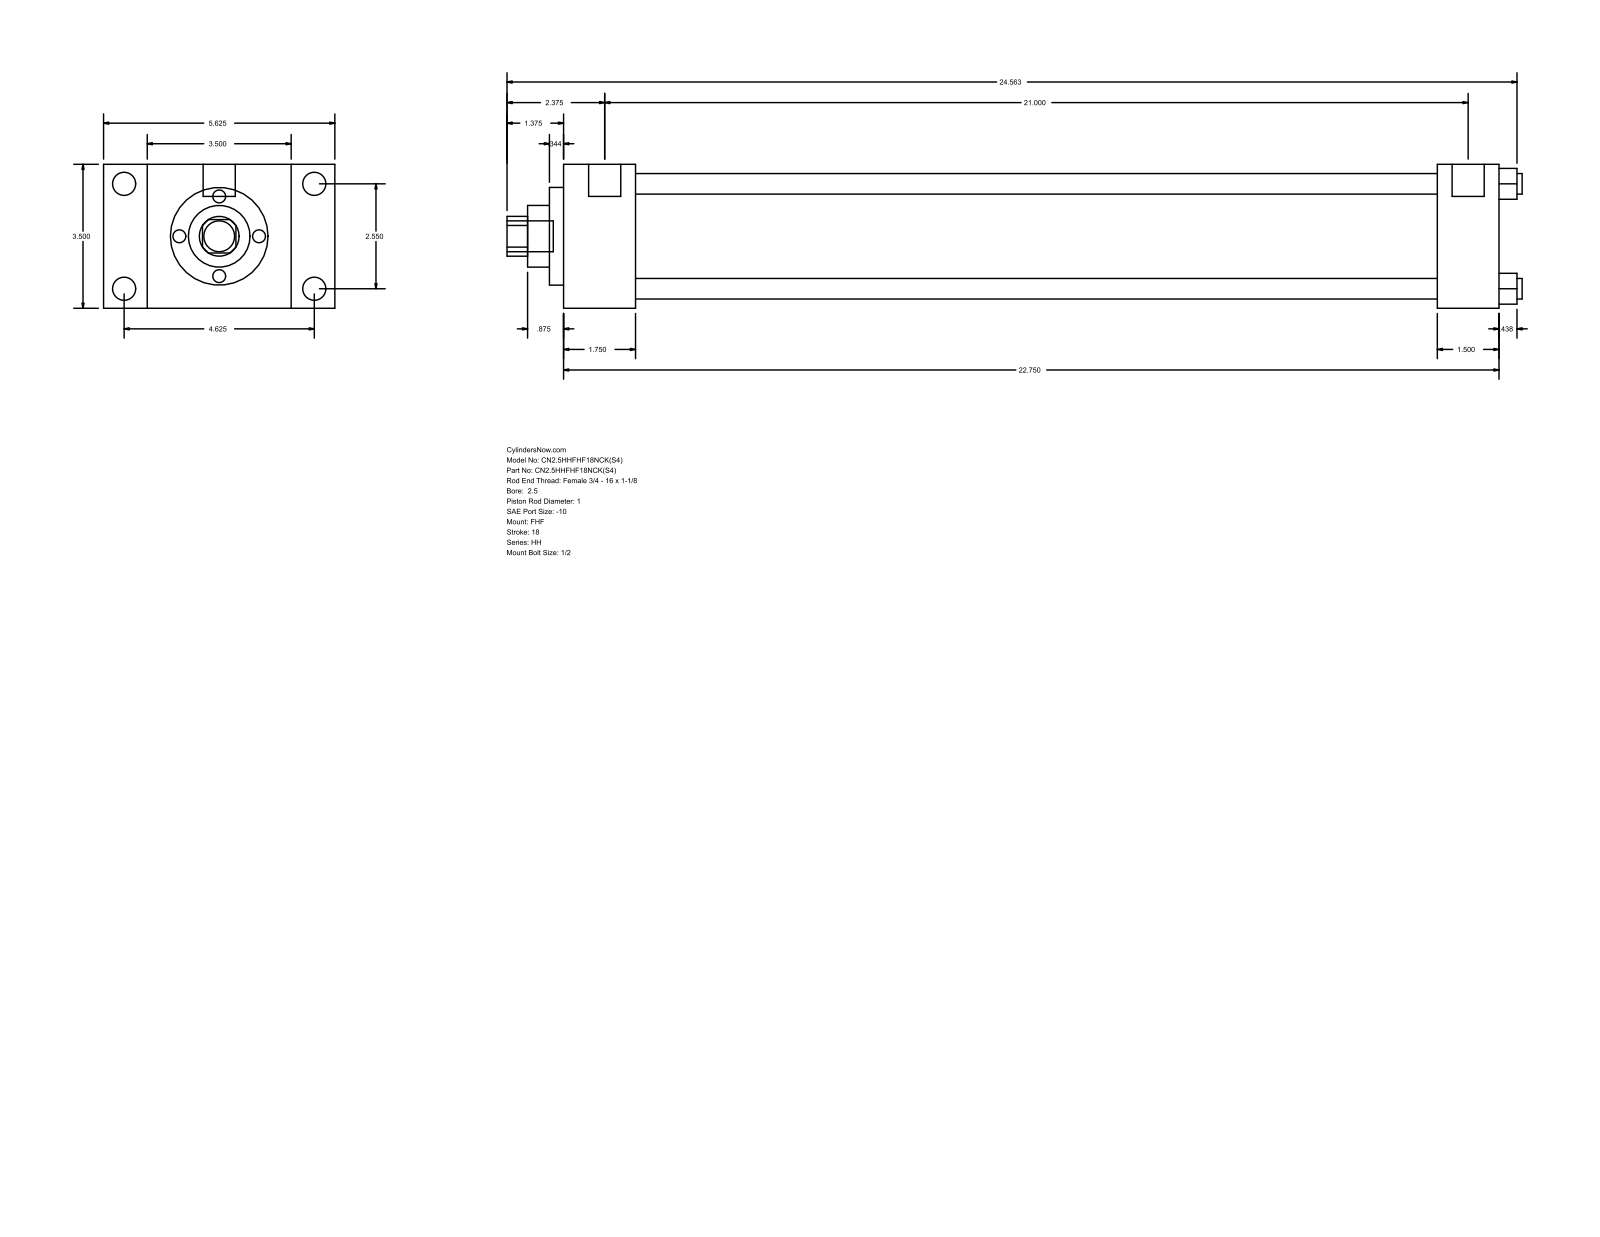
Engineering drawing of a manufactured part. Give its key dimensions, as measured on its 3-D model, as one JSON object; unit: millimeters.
{"part_name": "HH_FHF__0250_1", "step_written_by": "GSSL Pune (CONFIG_CONTROL_DESIGN)", "units": "millimeters", "bodies": {"solids": 0, "faces": 90, "planar": 61, "cylindrical": 29, "other": 0}, "overall_size": [627.06, 142.88, 88.9], "round_holes": [[12.7, 4], [25.4, 1], [38.1, 1], [60.33, 1], [73.03, 1]], "round_bosses_or_shafts": [[14.3, 4], [5.56, 4], [19.84, 2], [19.05, 1]], "partial_cylinders_radius": [[12.29, 1]], "face_to_face_distances": [88.9, 44.46, 26.99, 115.89, 577.85, 533.39, 142.88, 539.75, 495.29, 38.1], "hole_center_spacings": [45.79, 64.76, 91.58]}
